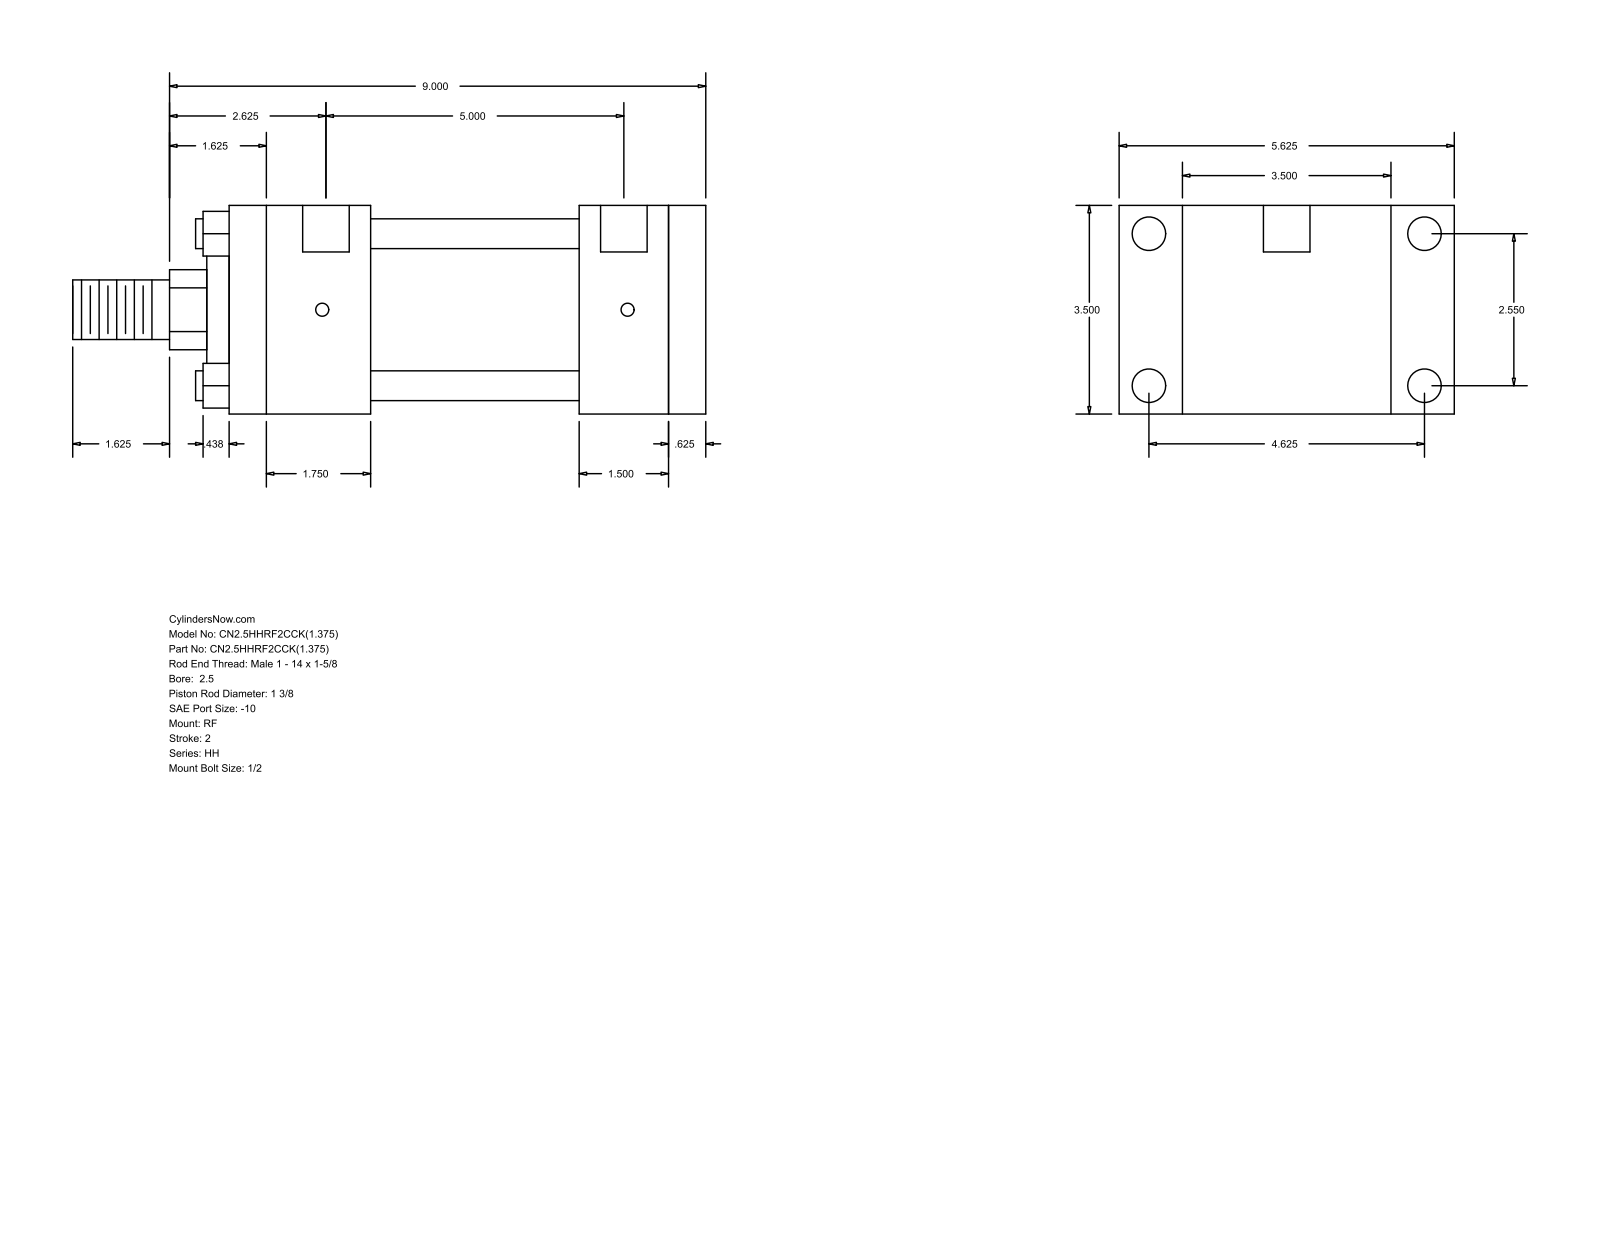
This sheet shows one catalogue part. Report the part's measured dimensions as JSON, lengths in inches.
{"part_name": "HH_RF__0250_1.375", "step_written_by": "GSSL Pune (CONFIG_CONTROL_DESIGN)", "units": "inches", "bodies": {"solids": 0, "faces": 92, "planar": 64, "cylindrical": 28, "other": 0}, "overall_size": [10.625, 5.625, 3.5], "round_holes": [[0.219, 4], [0.563, 4], [0.781, 2]], "round_bosses_or_shafts": [[0.5, 4], [2.875, 1], [2, 1], [1.375, 1], [1, 1]], "partial_cylinders_radius": [[0.672, 1]], "face_to_face_distances": [3.5, 5.625, 8, 0.625, 7.375, 2.375, 5, 5.875, 1.5, 2.125], "hole_center_spacings": [0.062, 2.55, 4.625, 5.063, 5.125, 5.281, 5]}
